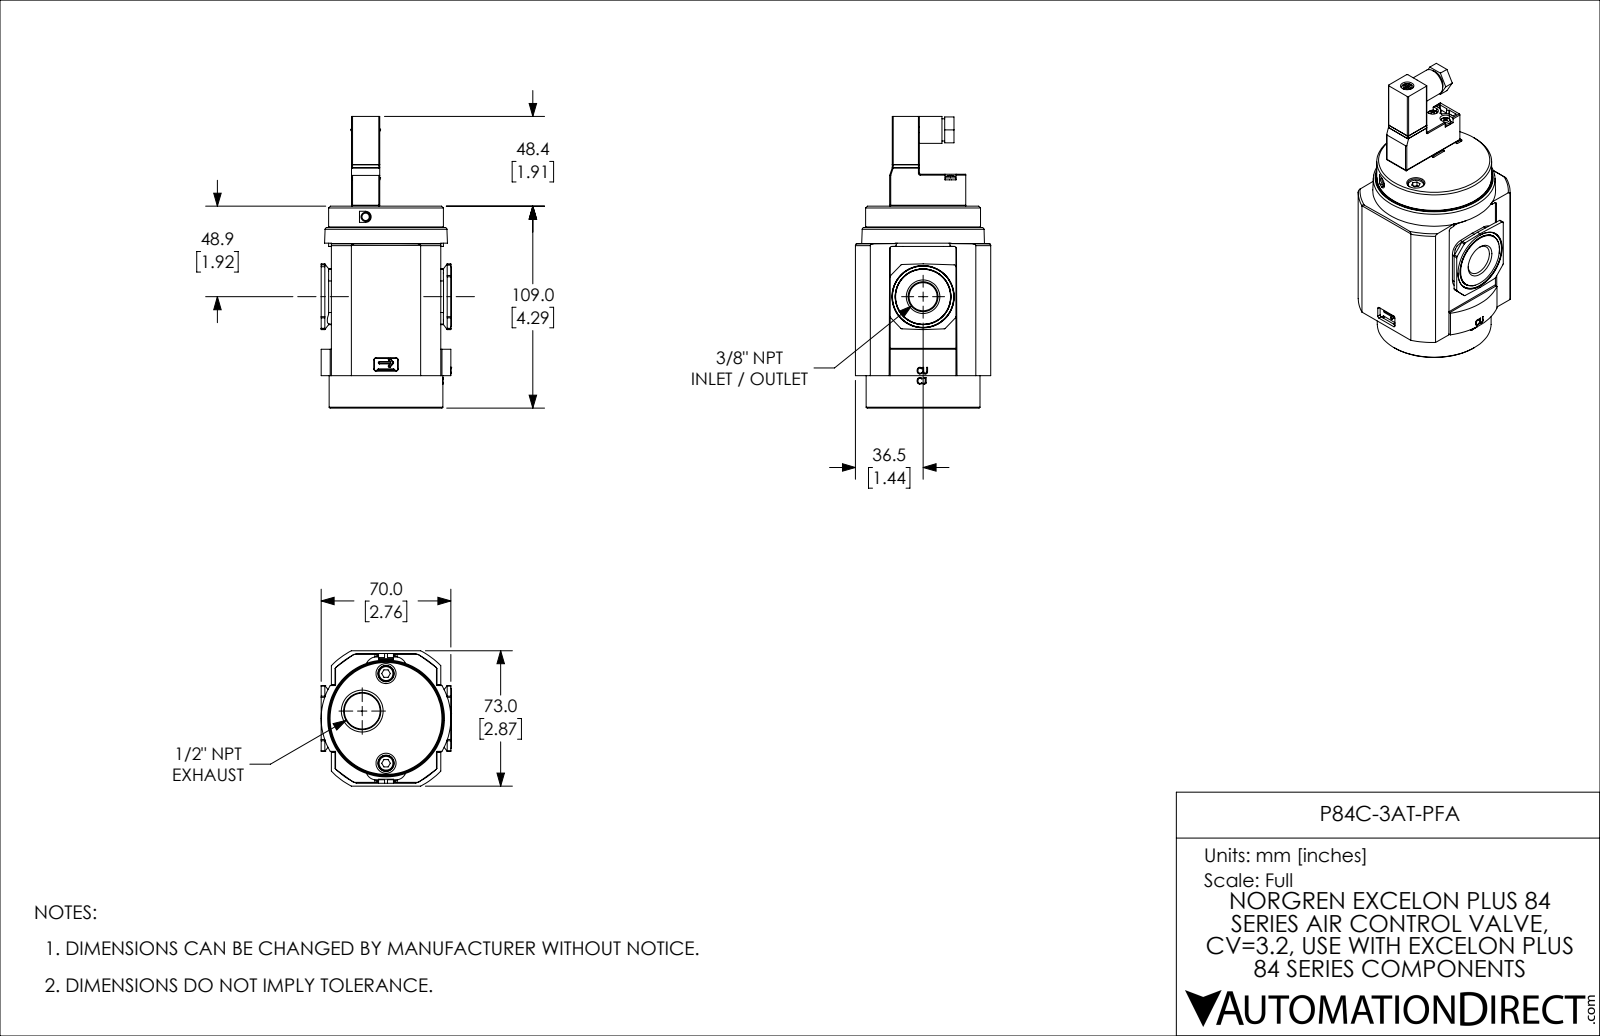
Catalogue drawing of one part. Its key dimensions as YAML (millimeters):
part_name: "P84C-3AT-PFA"
step_written_by: "SolidWorks 2021 (CONFIG_CONTROL_DESIGN)"
units: millimeters
bodies: {solids: 7, faces: 843, planar: 396, cylindrical: 250, other: 197}
overall_size: [157.35, 73, 70.25]
volume: 424368
surface_area: 95456
round_holes:
  - {diameter: 4.92, count: 4}
  - {diameter: 5.3, count: 4}
  - {diameter: 8.8, count: 4}
  - {diameter: 1.5, count: 3}
  - {diameter: 2.46, count: 3}
  - {diameter: 0.8, count: 2}
  - {diameter: 3.1, count: 2}
  - {diameter: 8.5, count: 2}
  - {diameter: 3.8, count: 1}
  - {diameter: 6.8, count: 1}
  - {diameter: 7.2, count: 1}
round_bosses_or_shafts:
  - {diameter: 8.5, count: 4}
  - {diameter: 5, count: 4}
  - {diameter: 3, count: 2}
  - {diameter: 62, count: 1}
  - {diameter: 61.4, count: 1}
  - {diameter: 59, count: 1}
  - {diameter: 14.5, count: 1}
  - {diameter: 12, count: 1}
partial_cylinders:
  - {radius: 0.5, count: 25}
  - {radius: 0.25, count: 14}
  - {radius: 1, count: 13}
  - {radius: 3, count: 4}
  - {radius: 6, count: 4}
  - {radius: 6.3, count: 4}
  - {radius: 0.55, count: 2}
  - {radius: 0.94, count: 2}
face_to_face_distances: [1.5, 70.2, 2, 71, 71.5, 69.5, 0.5, 70, 11.25, 81.45]
hole_center_spacings: [3.8, 5.05, 5.41, 7.11, 12.41, 24.88, 46.75, 1.41]
